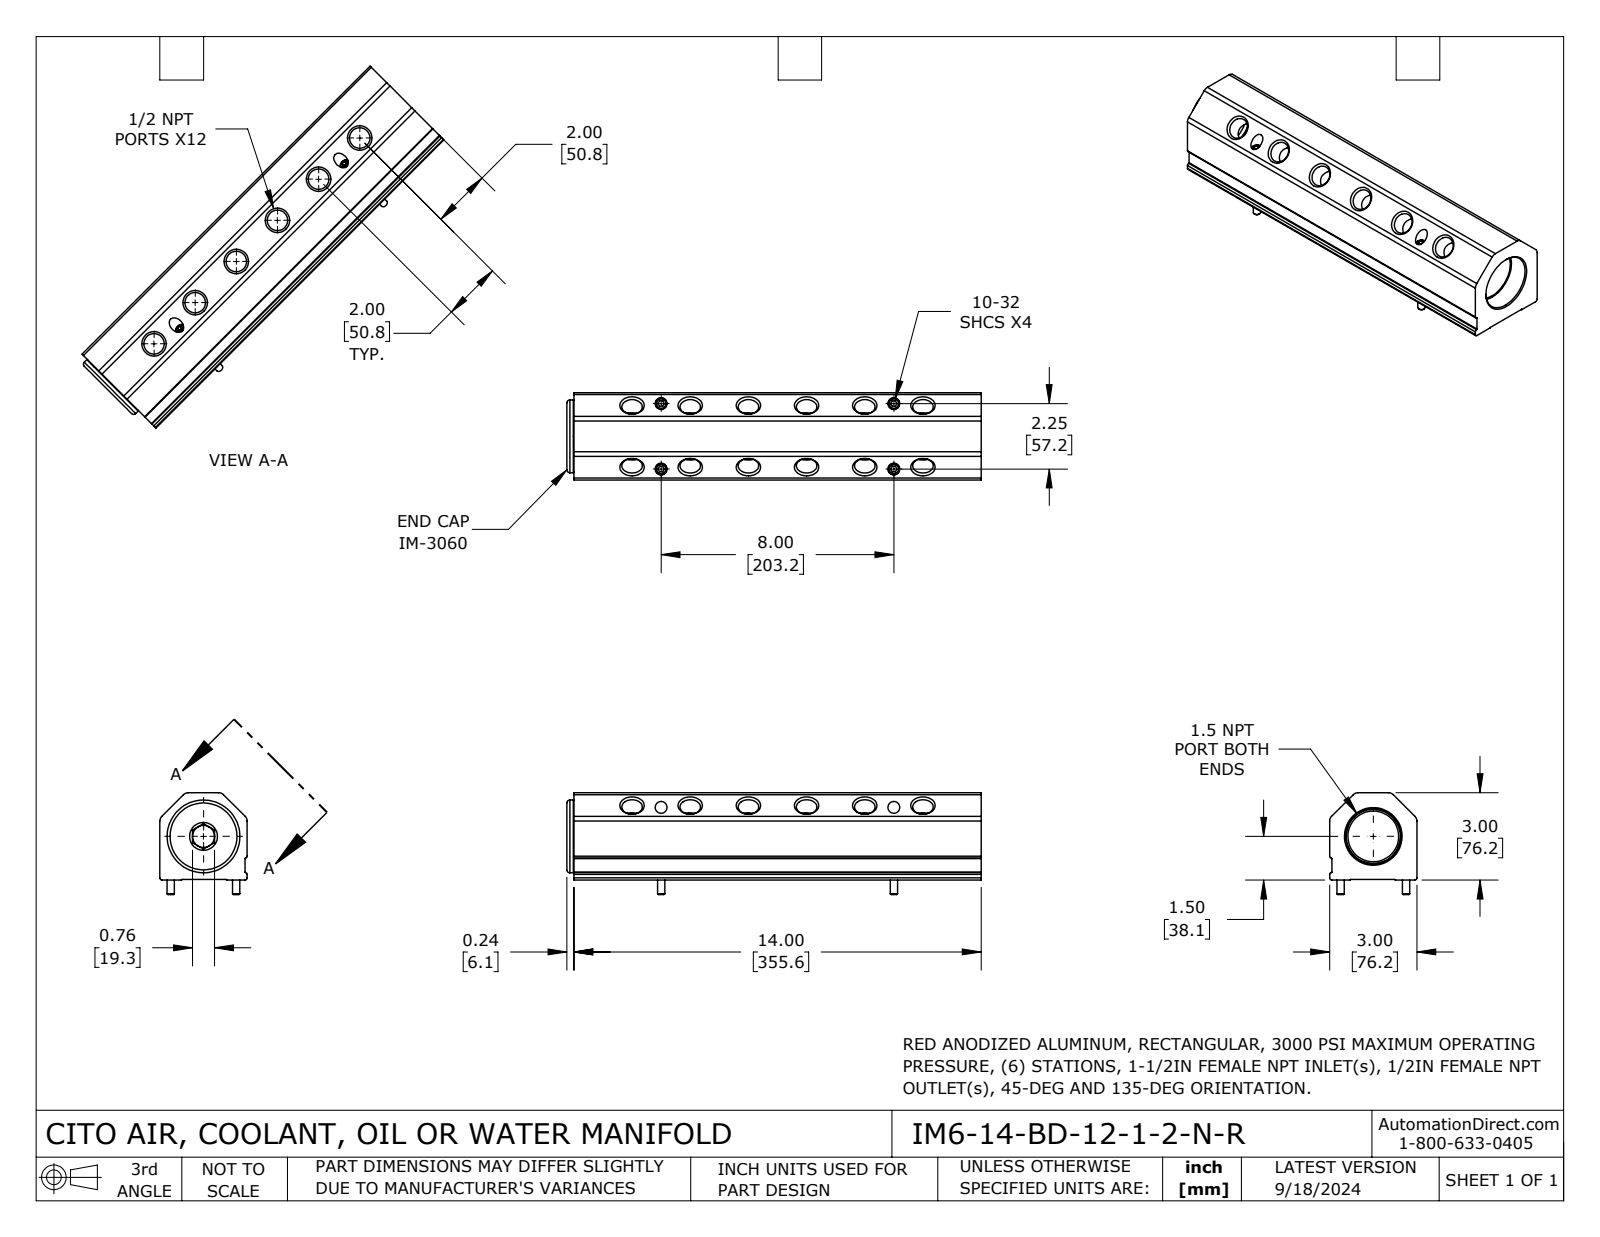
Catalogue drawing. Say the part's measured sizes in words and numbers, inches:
The part is named "IM6-14-BD-12-1-2-N-R". Its 3-D file was written by "SolidWorks 2023 (CONFIG_CONTROL_DESIGN)". It is 6 solids with 226 faces: 76 planar, 82 cylindrical and 68 other. Overall it measures 14.24 by 3.5 by 3 inches. Its volume is 79.16 cubic inches and its surface area 285.1 square inches. Round holes: 12 of diameter 0.703, 4 of diameter 0.266, 4 of diameter 0.406, 1 of diameter 0.758, 1 of diameter 1.743, 1 of diameter 2.262. Round bosses or shafts: 4 of diameter 0.375, 4 of diameter 0.25, 1 of diameter 2.5, 1 of diameter 1.984, 1 of diameter 1.761. Partial cylindrical surfaces (rounded edges, fillets, slot ends): 6 of radius 0.02, 4 of radius 0.225, 2 of radius 0.062, 2 of radius 0.075. The main face-to-face distances are 3, 0.02, 2.98, 0.075, 2.925, 14, 0.24, 14.24, 0.764, 0.524. The hole center spacings are 2, 4, 6, 8, 2.25, 8.31, 10.
